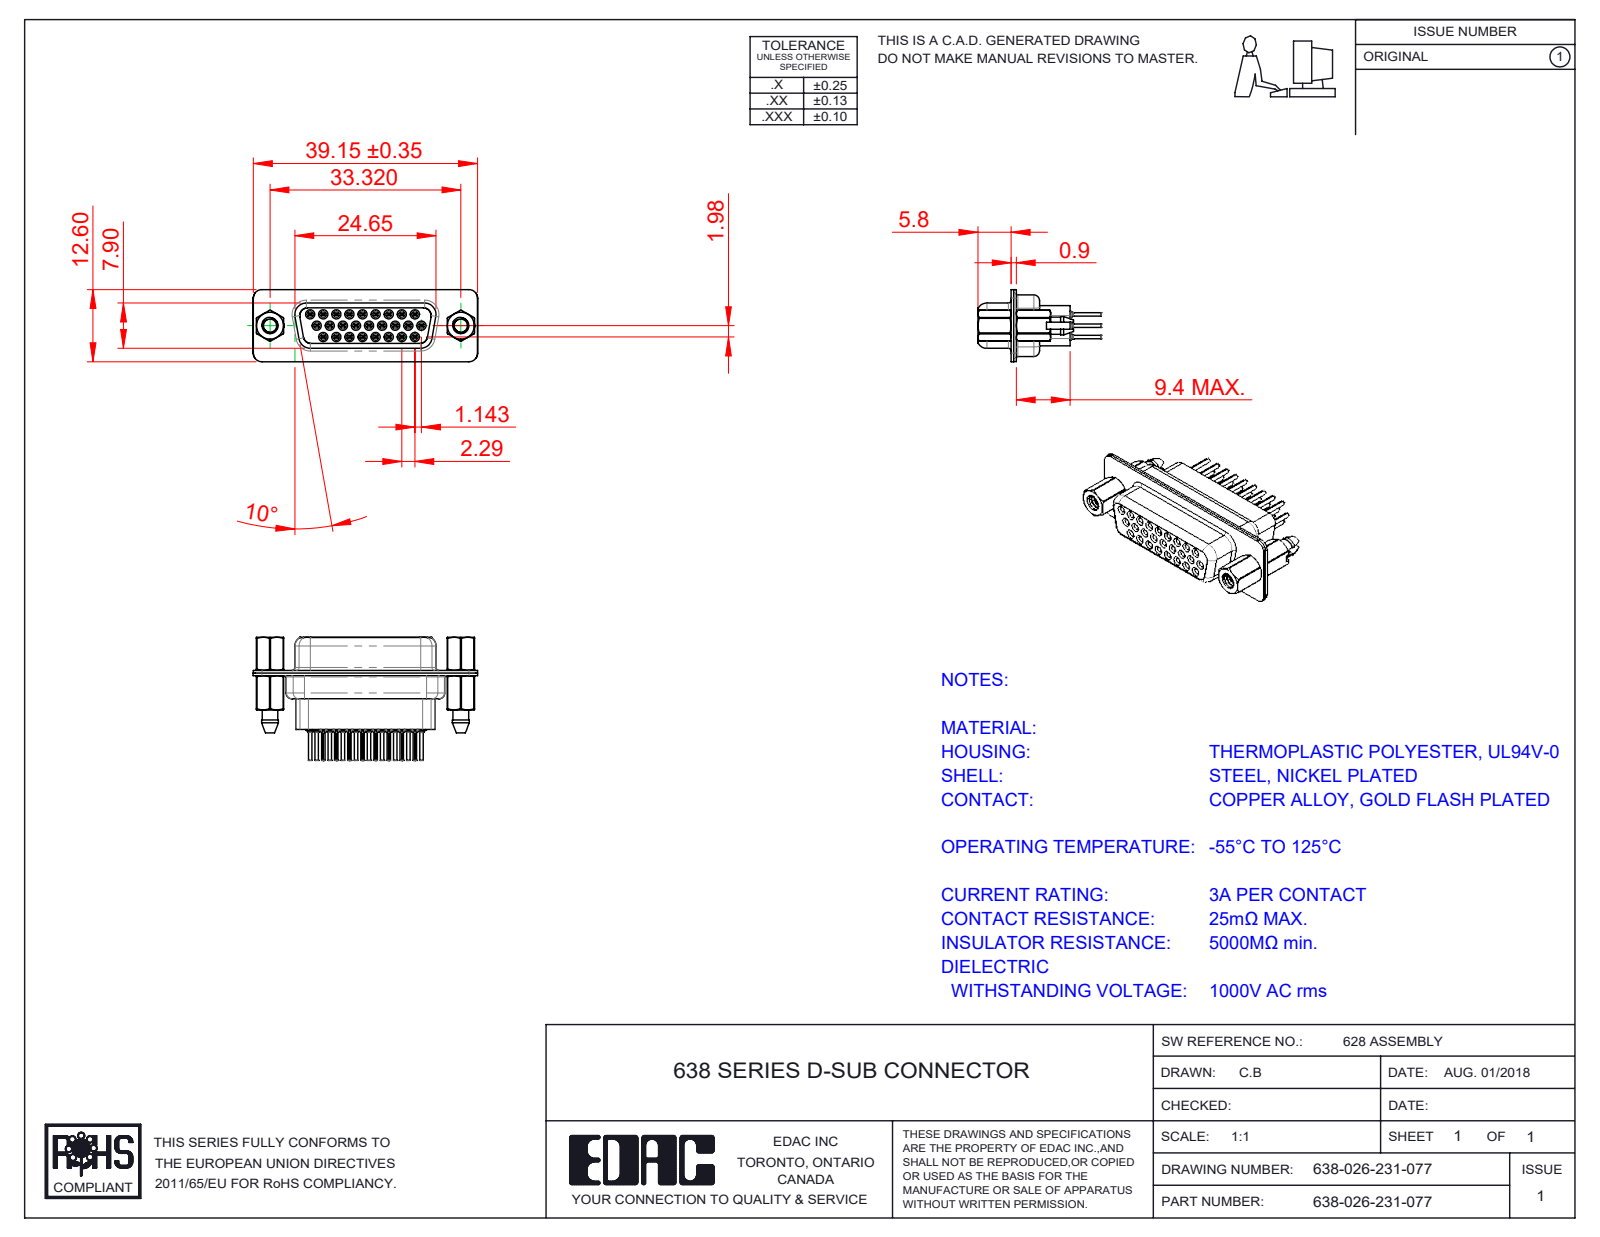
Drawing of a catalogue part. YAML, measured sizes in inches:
part_name: "638-026-231-077; 638 Shell Rear_26 Contacts; 638 Shell Front_26 Contacts; 638 Contact Row 2_31 (+5 more)"
step_written_by: "SolidWorks 2020 (CONFIG_CONTROL_DESIGN)"
units: inches
bodies: {solids: 33, faces: 3677, planar: 927, cylindrical: 1099, other: 1651}
overall_size: [1.543, 0.846, 0.496]
volume: 0.183
surface_area: 16.49
round_holes:
  - {diameter: 0.008, count: 26}
  - {diameter: 0.031, count: 26}
  - {diameter: 0.039, count: 26}
  - {diameter: 0.043, count: 26}
  - {diameter: 0.063, count: 26}
  - {diameter: 0.067, count: 26}
  - {diameter: 0.071, count: 26}
  - {diameter: 0.089, count: 2}
  - {diameter: 0.09, count: 2}
  - {diameter: 0.157, count: 2}
  - {diameter: 0.159, count: 2}
  - {diameter: 0.191, count: 2}
round_bosses_or_shafts:
  - {diameter: 0.079, count: 26}
  - {diameter: 0.059, count: 26}
  - {diameter: 0.047, count: 26}
  - {diameter: 0.024, count: 26}
  - {diameter: 0.195, count: 2}
  - {diameter: 0.189, count: 2}
  - {diameter: 0.11, count: 2}
partial_cylinders:
  - {radius: 0.004, count: 52}
  - {radius: 0.059, count: 22}
  - {radius: 0.011, count: 18}
  - {radius: 0.079, count: 12}
  - {radius: 0.061, count: 8}
  - {radius: 0.053, count: 5}
  - {radius: 0.01, count: 4}
  - {radius: 0.02, count: 4}
face_to_face_distances: [0.018, 0.016, 0.26, 0.056, 0.35, 0.035, 0.276, 0.187, 0.09, 0.228]
hole_center_spacings: [0.156, 0.09, 0.18, 0.238, 0.09, 0.324, 0.27, 0.413]
